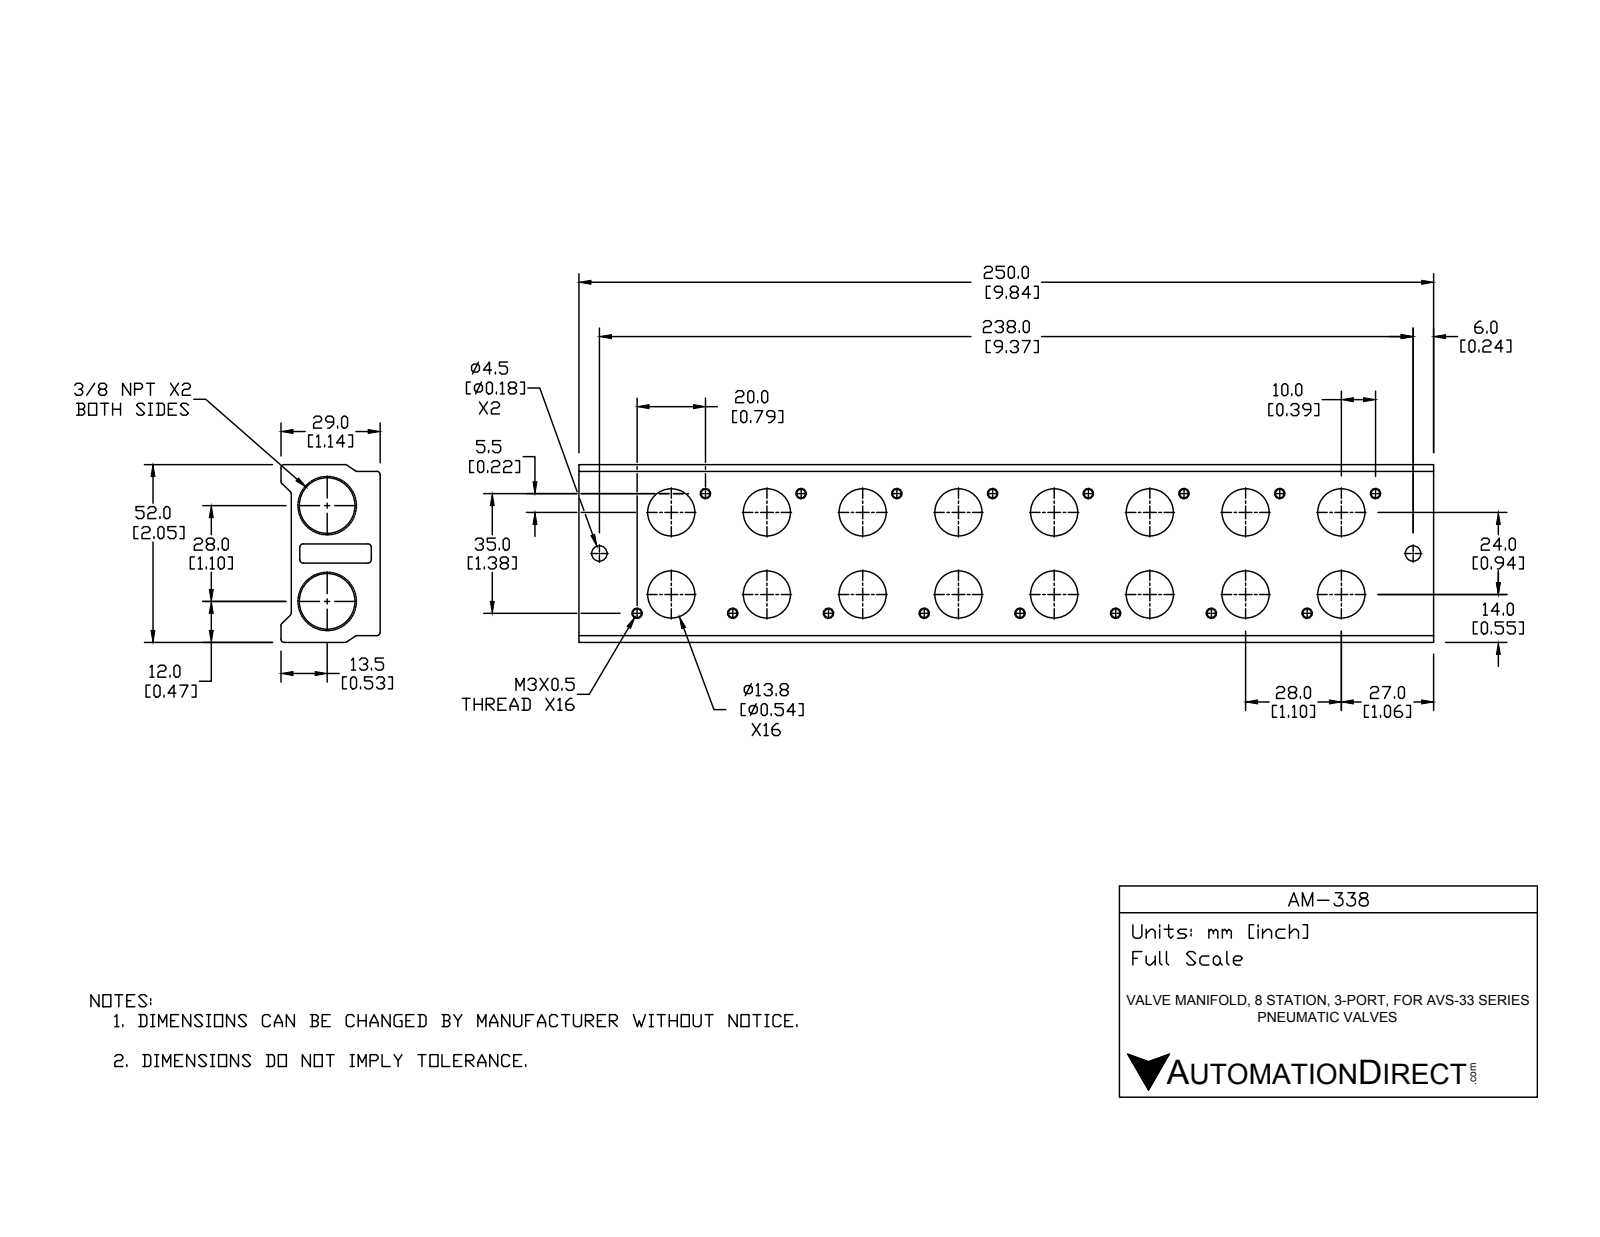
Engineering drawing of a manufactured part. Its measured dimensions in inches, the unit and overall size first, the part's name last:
Units: inches
Overall size (bounding box): 9.843 × 2.047 × 1.142
Round holes (diameter × count): ⌀0.098 ×16, ⌀0.543 ×16, ⌀0.177 ×2, ⌀0.437 ×2, ⌀0.562 ×2
Partial cylindrical surfaces — rounded edges, fillets, slot ends (radius × count): R0.039 ×16
Main face-to-face distances: 0.913, 1.134, 1.024, 0.22, 2.047, 0.079, 1.969, 0.835, 1.055, 0.118
Hole centre spacings: 1.102, 2.205, 3.307, 0.449, 1.226, 4.409, 0.741, 1.361
Volume: 13.75 in³ · Surface area: 121 in²
Bodies: 1 solid, 210 faces (26 planar, 108 cylindrical, 76 other)
Part name (STEP PRODUCT): AM-338
STEP written by: SolidWorks 2016 (AUTOMOTIVE_DESIGN)
